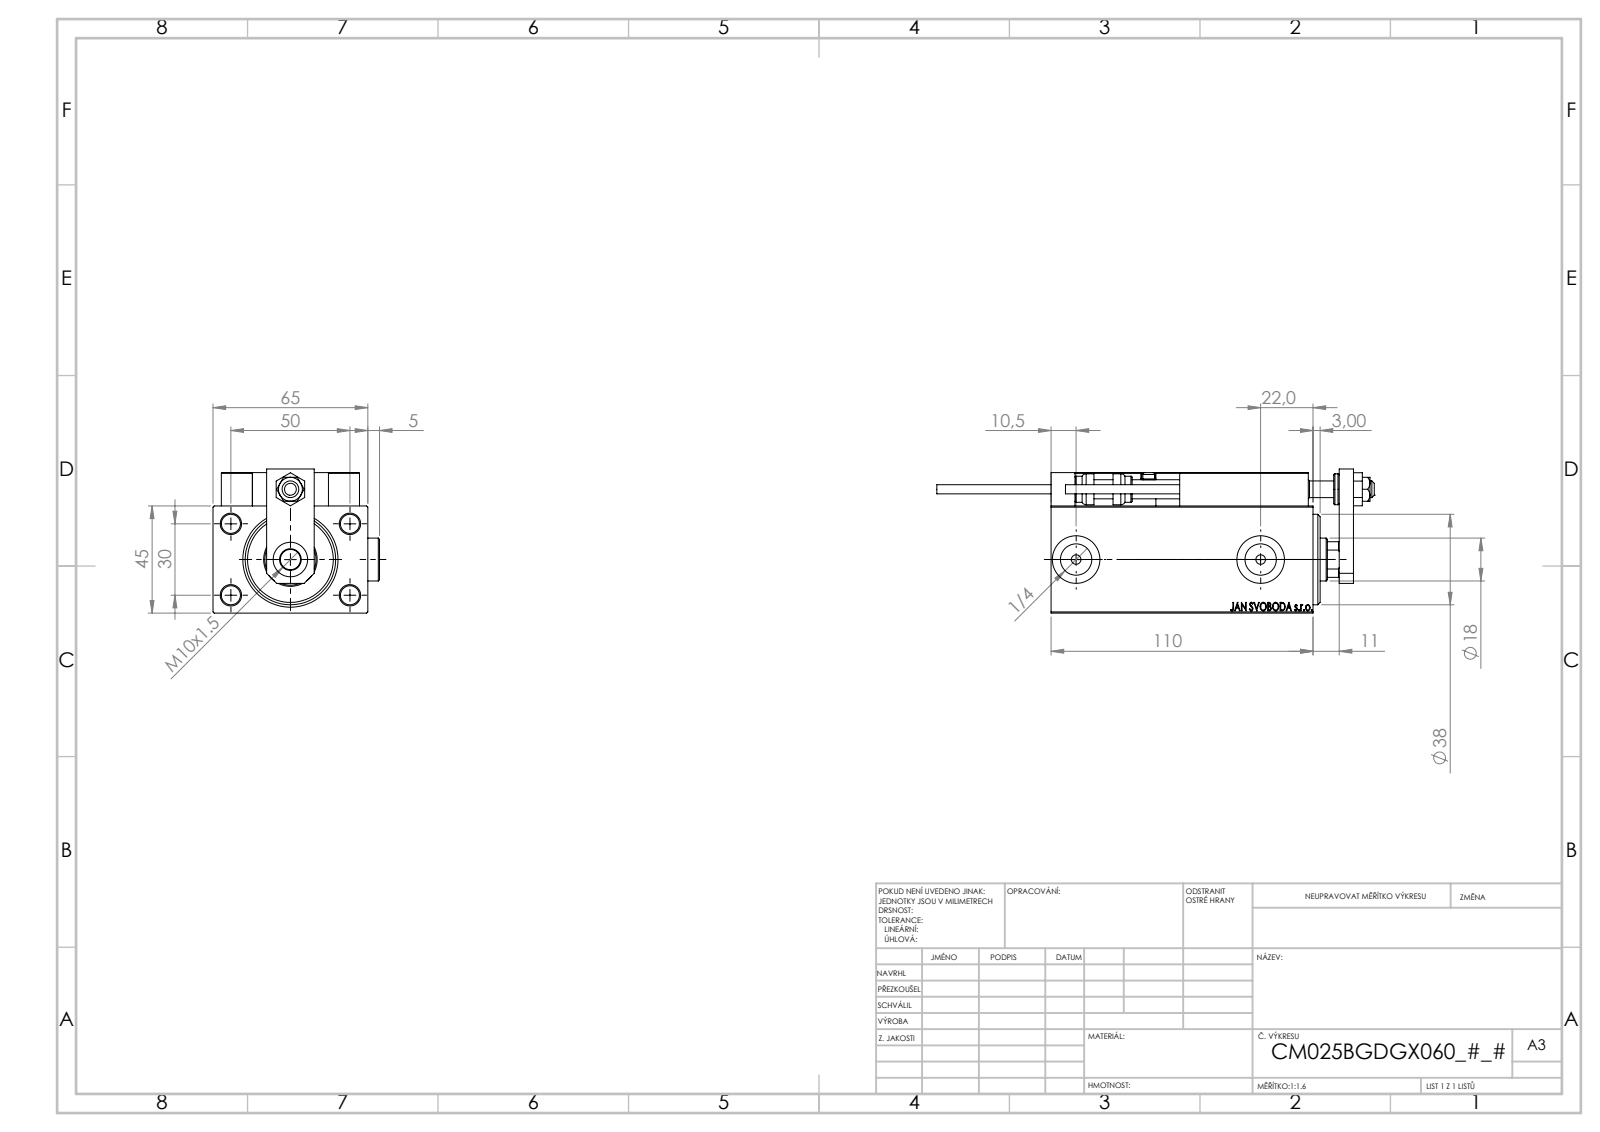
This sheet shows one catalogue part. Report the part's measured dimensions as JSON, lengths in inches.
{"part_name": "ZARAZKA; SWITCH_X_FRONT_BACK; V450CM_B_VCP; NUT_D10 (+8 more)", "step_written_by": "SolidWorks 2019 (CONFIG_CONTROL_DESIGN)", "units": "inches", "bodies": {"solids": 26, "faces": 1372, "planar": 595, "cylindrical": 200, "other": 577}, "overall_size": [7.232, 2.752, 2.382], "volume_in3": 21.18, "surface_area_in2": 127.7, "round_holes": [[0.315, 9], [0.157, 6], [0.126, 4], [0.197, 2], [0.518, 2], [0.787, 2], [0.276, 1], [0.335, 1], [0.571, 1], [0.709, 1], [0.846, 1], [0.886, 1]], "round_bosses_or_shafts": [[0.709, 2], [0.197, 2], [0.15, 2], [0.512, 1], [0.433, 1]], "partial_cylinders_radius": [[0.012, 30], [0.118, 2], [0.335, 1]], "face_to_face_distances": [1.772, 2.559, 0.551, 0.236, 2.323, 0.197, 0.512, 0.138, 4.764, 0.748], "hole_center_spacings": [1.148, 0.448, 0.787, 1.138, 1.165, 1.169, 1.181, 1.42]}
